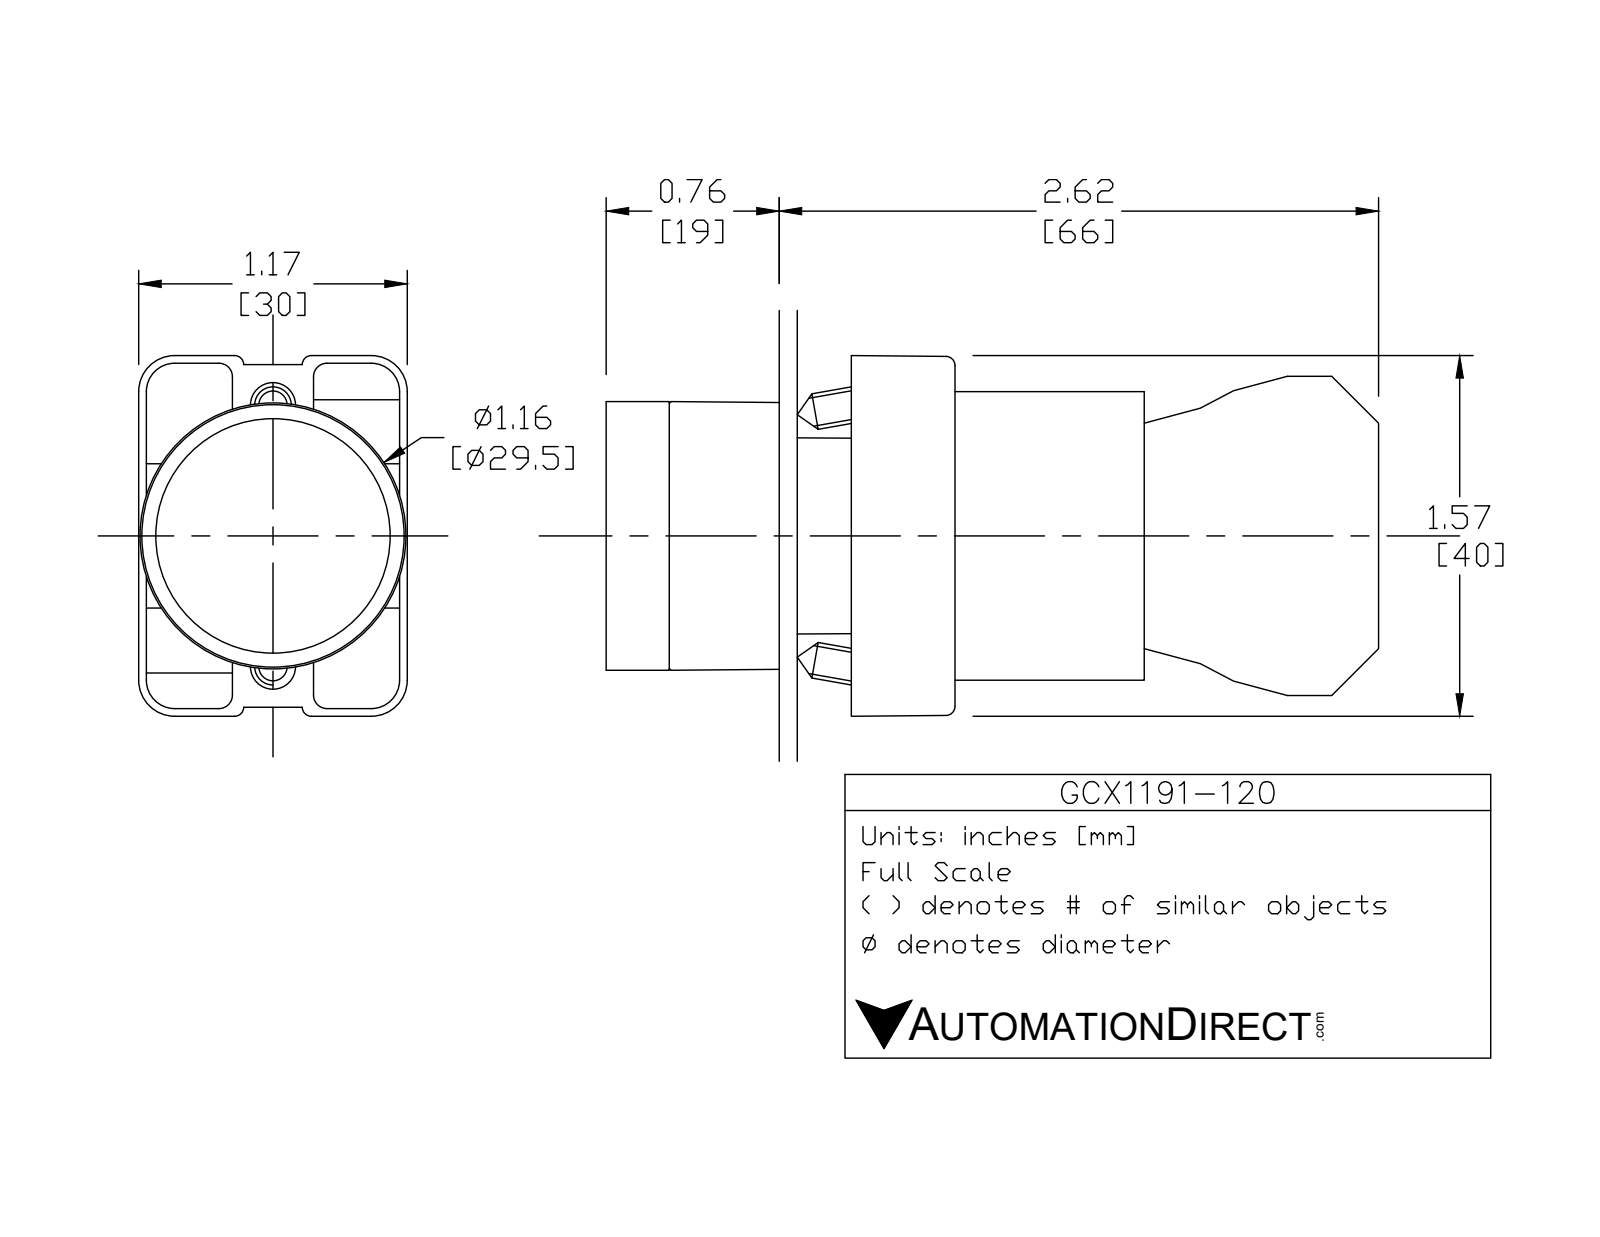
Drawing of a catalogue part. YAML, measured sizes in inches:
part_name: "GCX1191 OPERATOR; ecx1029; ecx1040; GCX1191-120 (+1 more)"
step_written_by: "SolidWorks 2016 (AUTOMOTIVE_DESIGN)"
units: inches
bodies: {solids: 8, faces: 431, planar: 252, cylindrical: 148, other: 31}
overall_size: [3.319, 1.581, 1.177]
volume: 2.794
surface_area: 38.75
round_holes:
  - {diameter: 0.079, count: 2}
  - {diameter: 0.124, count: 2}
  - {diameter: 0.13, count: 2}
  - {diameter: 0.087, count: 1}
  - {diameter: 0.197, count: 1}
  - {diameter: 0.469, count: 1}
  - {diameter: 0.878, count: 1}
  - {diameter: 0.888, count: 1}
  - {diameter: 1.024, count: 1}
round_bosses_or_shafts:
  - {diameter: 0.157, count: 4}
  - {diameter: 1.175, count: 1}
  - {diameter: 1.004, count: 1}
  - {diameter: 0.945, count: 1}
  - {diameter: 0.856, count: 1}
  - {diameter: 0.78, count: 1}
  - {diameter: 0.504, count: 1}
partial_cylinders:
  - {radius: 0.059, count: 24}
  - {radius: 0.041, count: 12}
  - {radius: 0.124, count: 12}
  - {radius: 0.157, count: 12}
  - {radius: 0.039, count: 8}
  - {radius: 0.128, count: 2}
  - {radius: 0.02, count: 1}
  - {radius: 0.063, count: 1}
face_to_face_distances: [0.827, 2.02, 1.193, 0.579, 1.171, 0.031, 0.276, 0.033, 0.748, 0.573]
hole_center_spacings: [0.236, 0.544, 0.472, 0.49]
